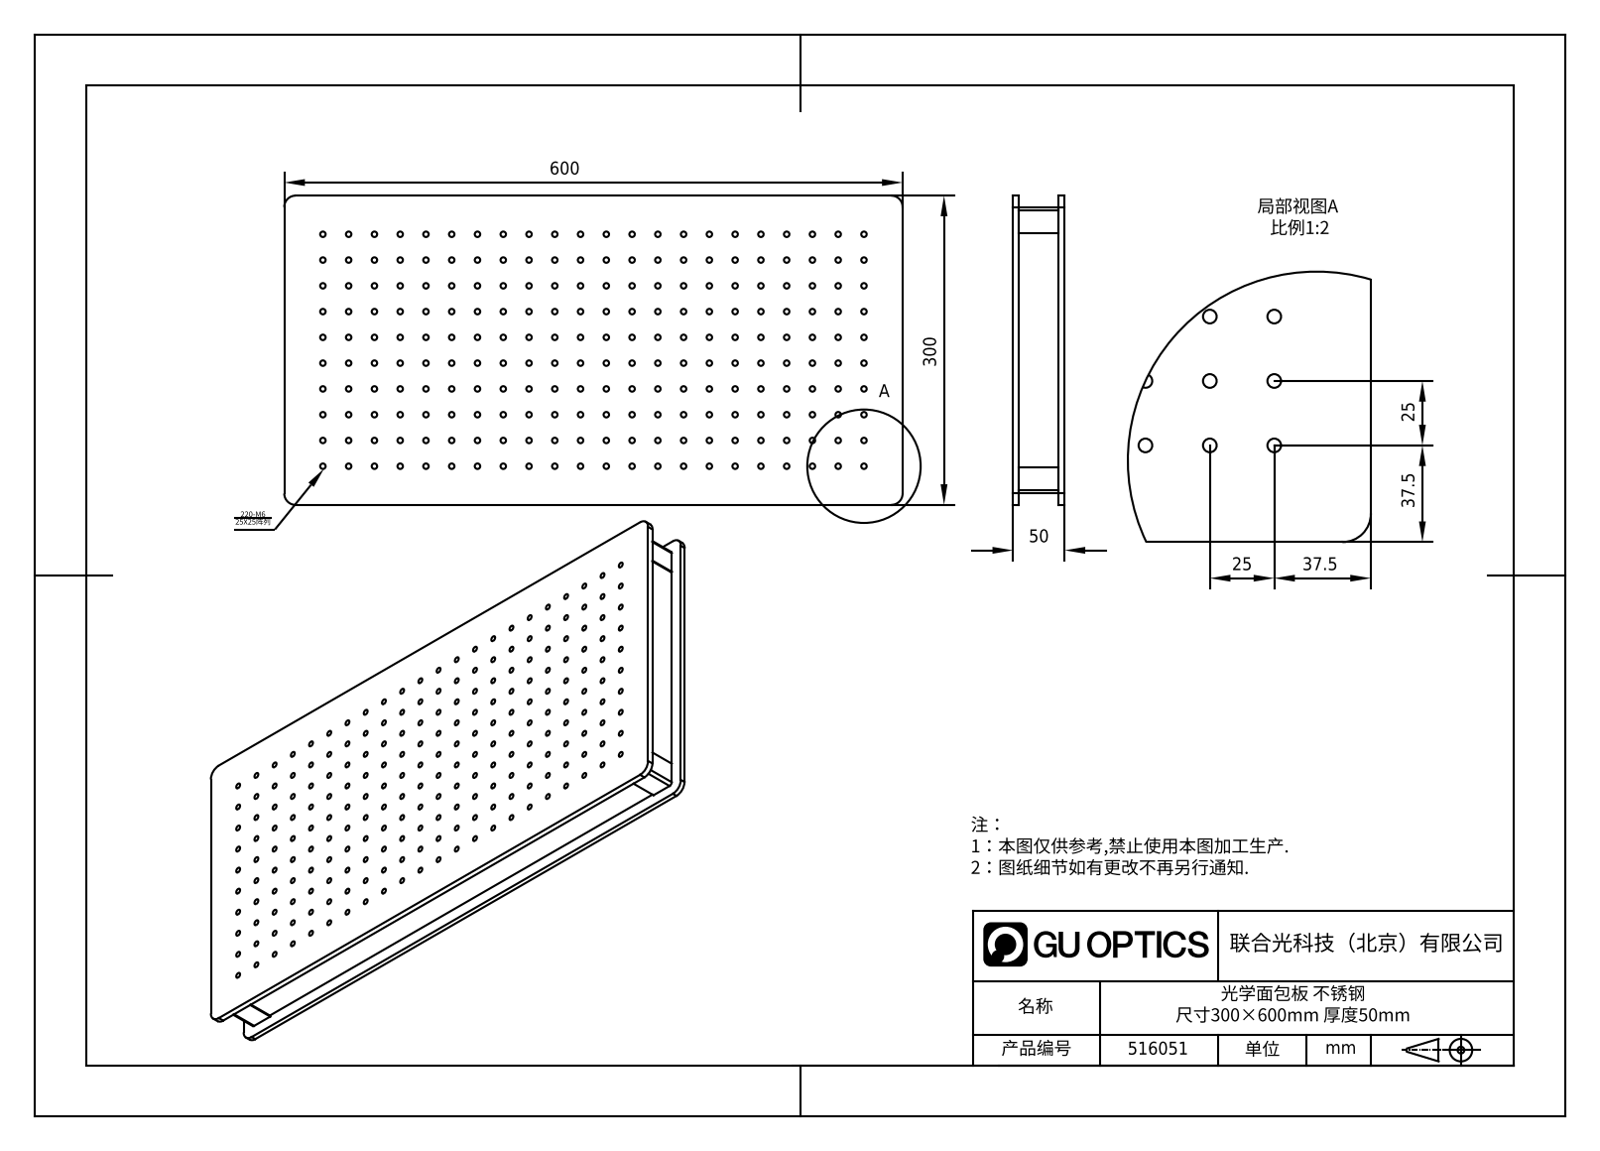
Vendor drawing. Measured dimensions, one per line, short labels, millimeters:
name: 516051
written by: SolidWorks 2020 (CONFIG_CONTROL_DESIGN)
unit: mm
bodies: 1 solid, 720 faces (264 planar, 456 cylindrical, 0 other)
size: 600 × 300 × 50
volume: 8 091 000 mm³; area: 520 964 mm²
holes: 220× ⌀5.3
rounds: 4× R2, 4× R3, 4× R11
face distances: 50, 6, 44, 45, 39, 5, 274, 13, 287, 1
hole spacings: 55.9, 25, 35.36, 50, 79.06, 103.08, 75, 90.14
